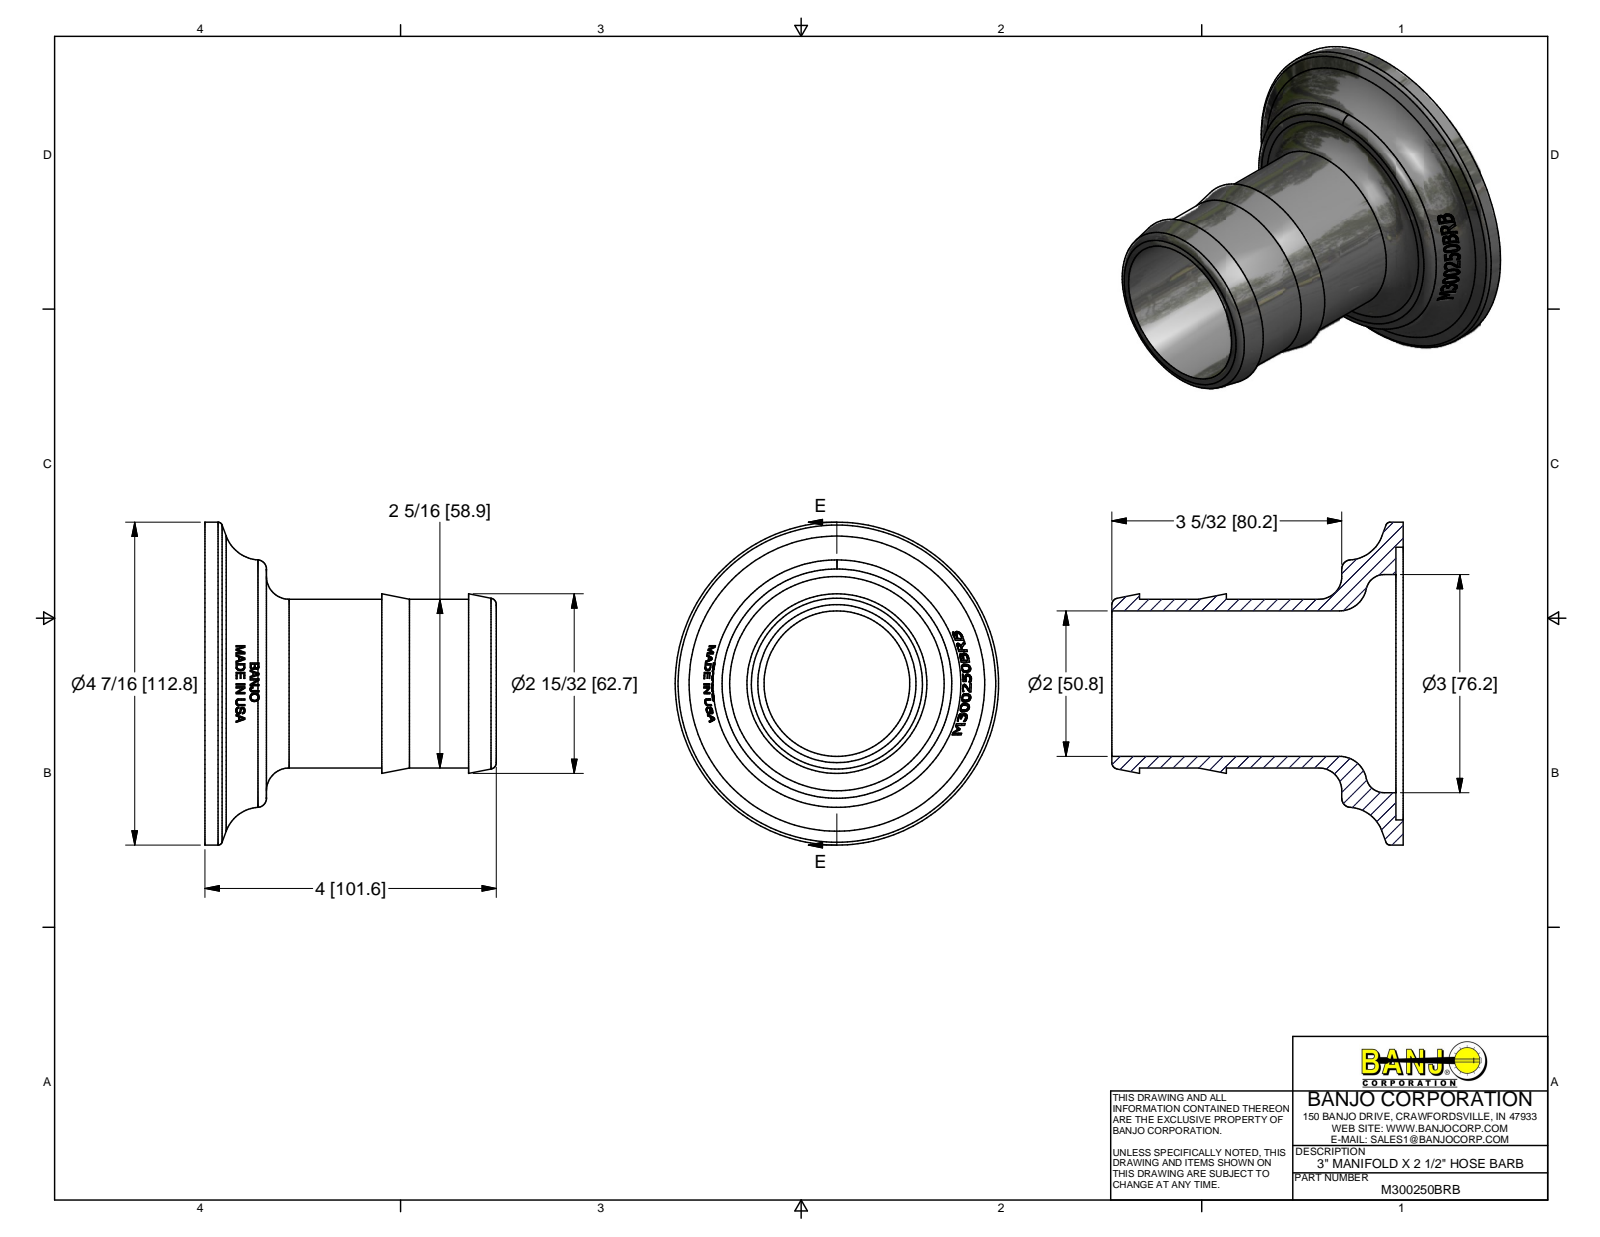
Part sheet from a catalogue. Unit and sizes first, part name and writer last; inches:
Units: inches
Overall size (bounding box): 4.44 × 4.44 × 4
Round holes (diameter × count): ⌀2 ×1, ⌀3 ×1, ⌀3.75 ×1
Round bosses / shafts (diameter × count): ⌀4.44 ×1, ⌀2.32 ×1
Main face-to-face distances: 0.1, 0.844, 0.744, 0.38, 3.156, 2.428, 3.62, 2.328, 3.52, 1.584
Volume: 8.528 in³ · Surface area: 80.23 in²
Bodies: 1 solid, 420 faces (184 planar, 6 cylindrical, 230 other)
Part name (STEP PRODUCT): M300250BRB
STEP written by: Autodesk Inventor 2014 (AUTOMOTIVE_DESIGN)
